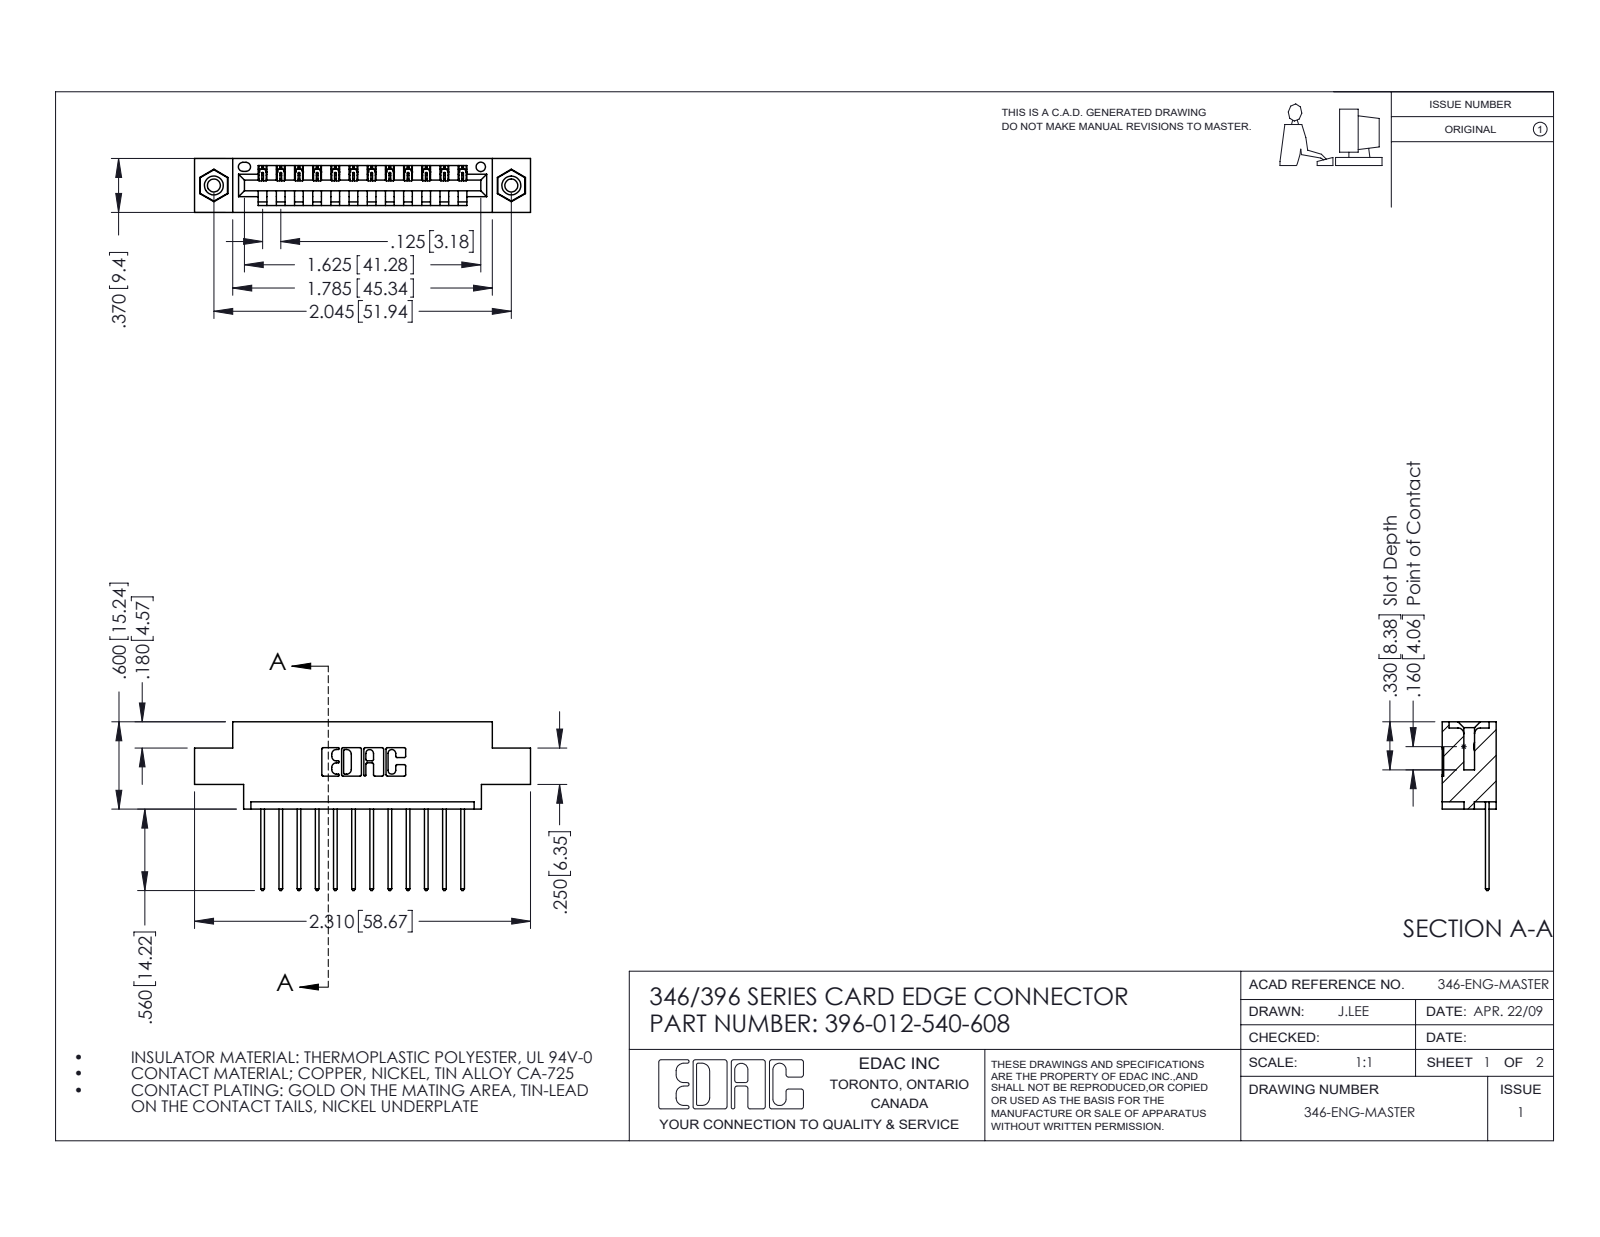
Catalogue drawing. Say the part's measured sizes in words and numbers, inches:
The part is named "345-250-001_345-250-003-102; 345-292-001_345-293-140; 396-012-540-608; 346 Part_0.170 Offset - 0.156 Dia-TI". Its 3-D file was written by "SolidWorks 2016 (CONFIG_CONTROL_DESIGN)". It is 15 solids with 882 faces: 592 planar, 274 cylindrical and 16 other. Overall it measures 2.31 by 1.16 by 0.37 inches. Its volume is 0.321 cubic inches and its surface area 10.16 square inches. Round holes: 2 of diameter 0.089, 2 of diameter 0.125, 2 of diameter 0.156, 1 of diameter 0.064. Round bosses or shafts: 2 of diameter 0.155. Partial cylindrical surfaces (rounded edges, fillets, slot ends): 24 of radius 0.006, 24 of radius 0.01, 22 of radius 0.01, 6 of radius 0.007, 6 of radius 0.031, 3 of radius 0.026, 2 of radius 0.031, 2 of radius 0.04. The main face-to-face distances are 0.25, 0.048, 0.322, 0.37, 0.072, 0.298, 0.025, 0.222, 0.148, 0.1. The hole center spacings are 0.246, 1.839, 2.045.
